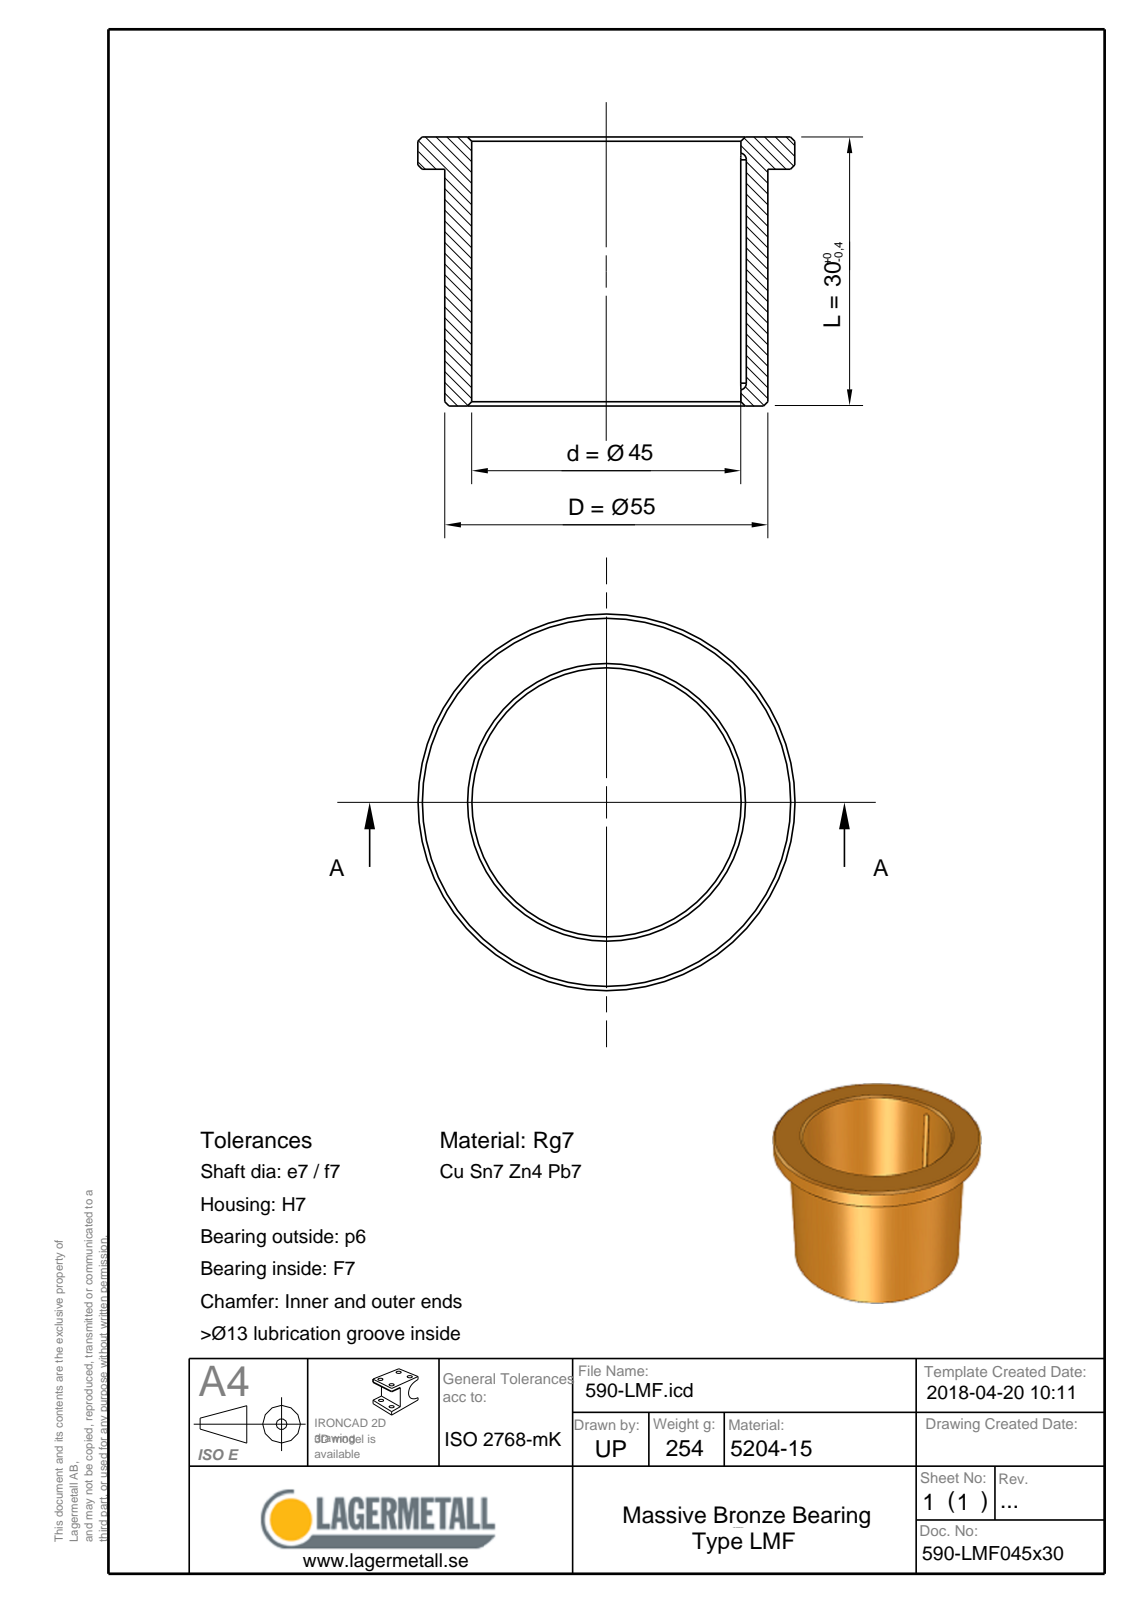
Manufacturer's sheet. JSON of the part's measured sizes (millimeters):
{"part_name": "590-LMF045x30", "step_written_by": "Spatial InterOp 3D (CONFIG_CONTROL_DESIGN)", "units": "millimeters", "bodies": {"solids": 1, "faces": 16, "planar": 4, "cylindrical": 5, "other": 7}, "overall_size": [65, 65, 30], "volume_mm3": 28897, "surface_area_mm2": 12689, "round_holes": [[45, 1]], "round_bosses_or_shafts": [[65, 1], [55, 1]], "partial_cylinders_radius": [[1.25, 2]], "face_to_face_distances": [6, 24, 30]}
